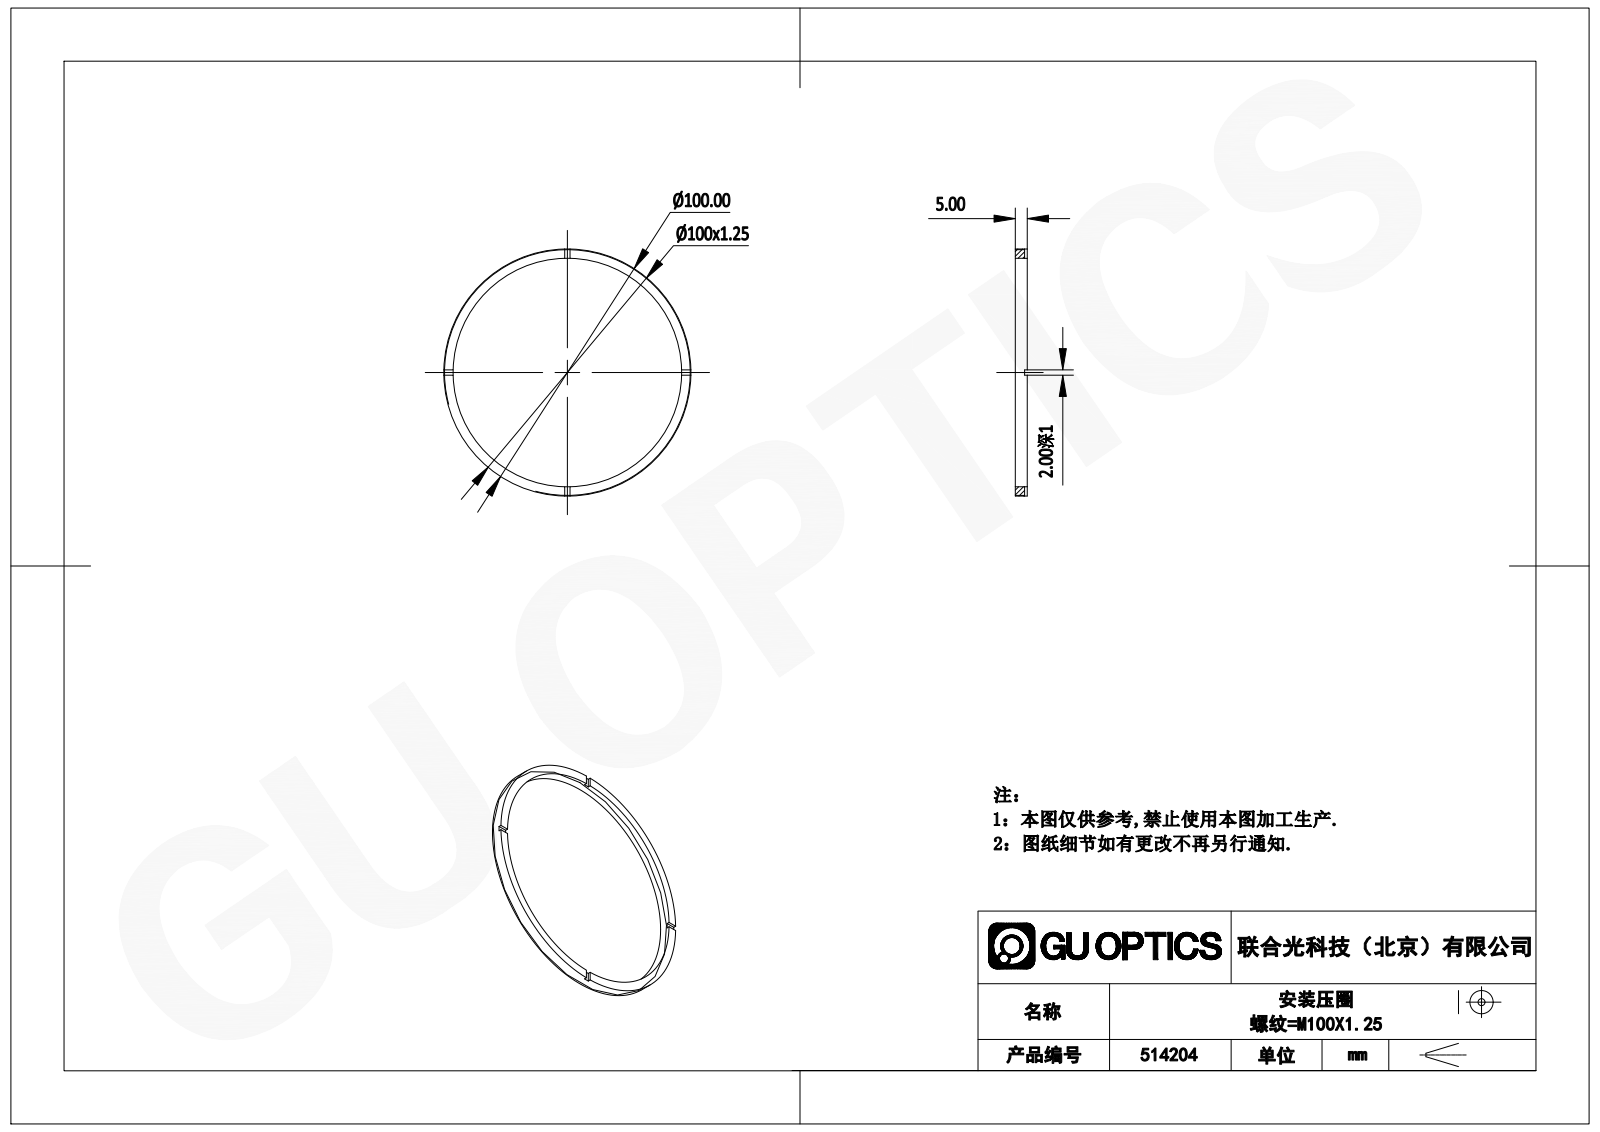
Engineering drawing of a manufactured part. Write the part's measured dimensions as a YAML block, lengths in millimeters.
part_name: "514204"
step_written_by: "SolidWorks 2020 (CONFIG_CONTROL_DESIGN)"
units: millimeters
bodies: {solids: 1, faces: 21, planar: 17, cylindrical: 4, other: 0}
overall_size: [100, 100, 5]
volume: 6000
surface_area: 5445
round_holes:
  - {diameter: 92, count: 1}
round_bosses_or_shafts:
  - {diameter: 100, count: 1}
face_to_face_distances: [5, 4, 1, 2]
